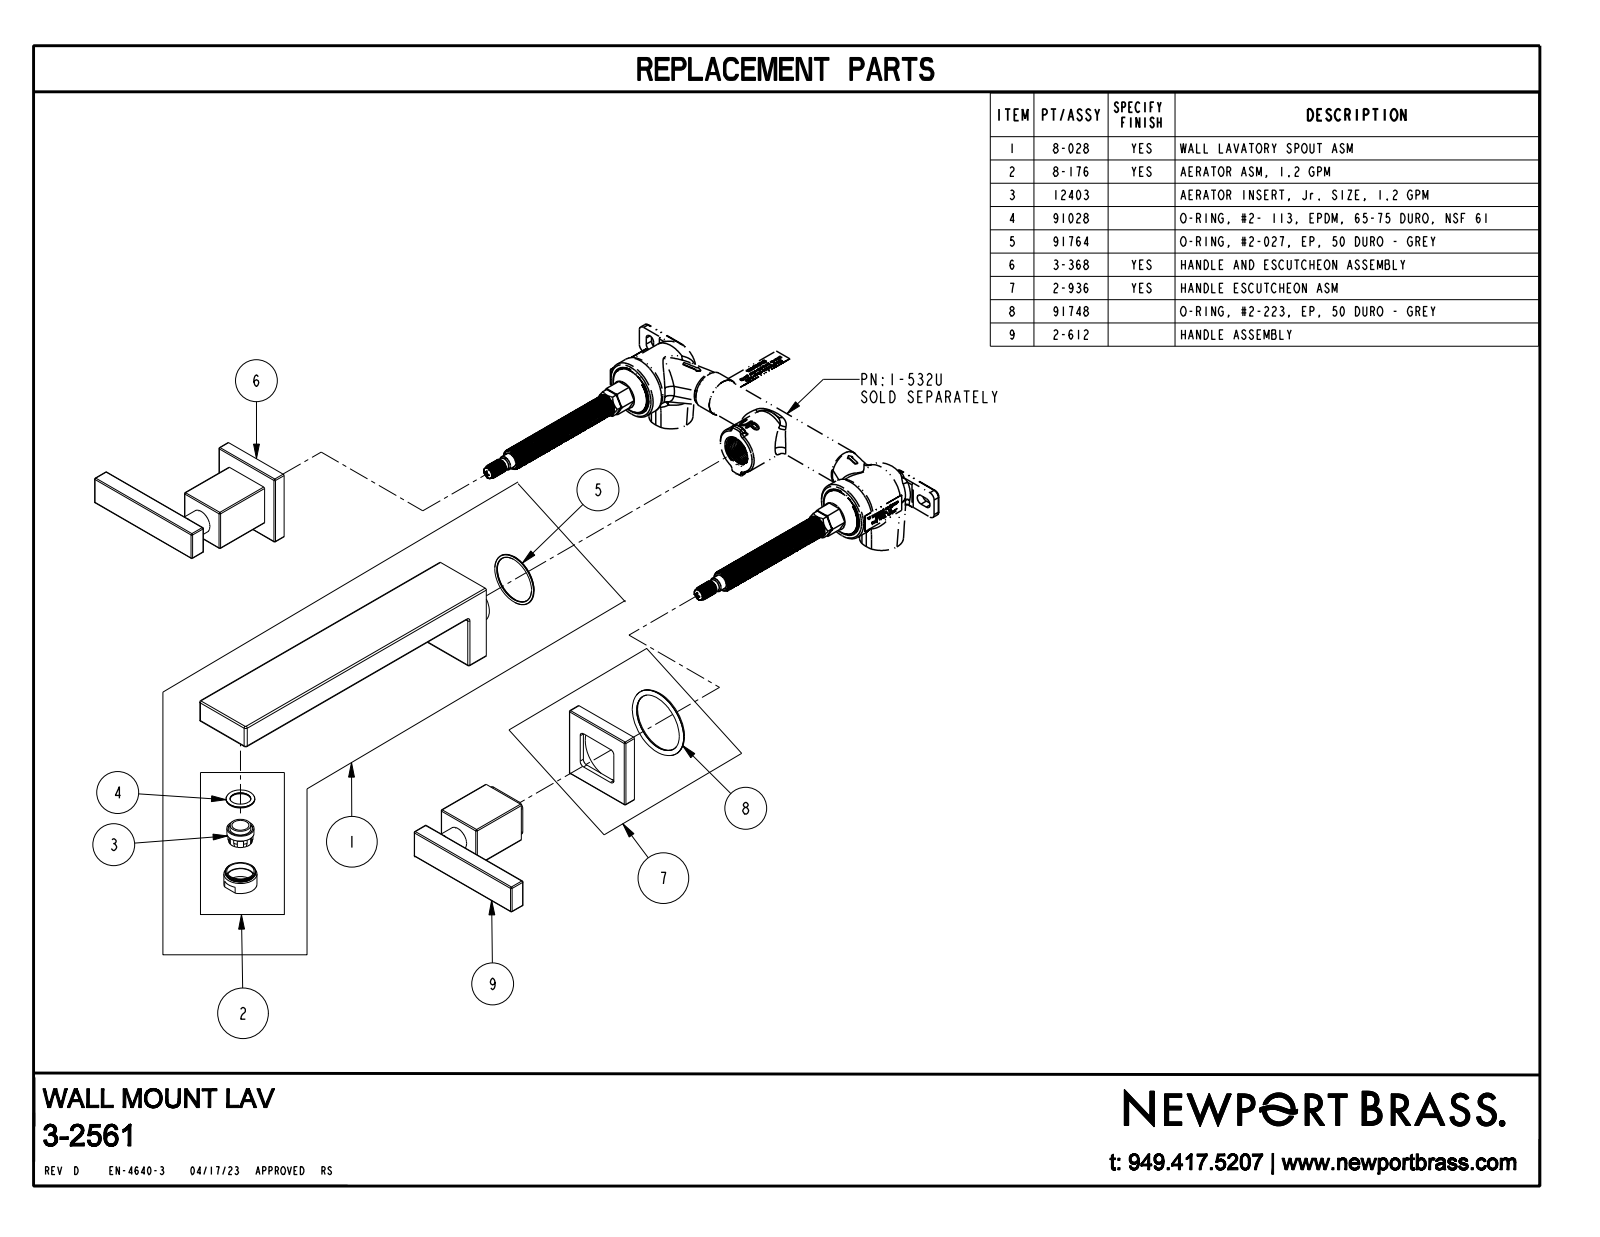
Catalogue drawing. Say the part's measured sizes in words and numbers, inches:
The part is named "3-2561_SW0001". Its 3-D file was written by "CREO PARAMETRIC BY PTC INC, 2018400 (AUTOMOTIVE_DESIGN)". It is 3 solids with 189 faces: 53 planar, 88 cylindrical and 48 other. Overall it measures 13.876 by 9.438 by 2.2 inches. Its volume is 23.84 cubic inches and its surface area 114.1 square inches. Round bosses or shafts: 2 of diameter 0.65, 2 of diameter 0.523, 1 of diameter 1.65, 1 of diameter 1.1, 1 of diameter 0.875. Partial cylindrical surfaces (rounded edges, fillets, slot ends): 48 of radius 0.03, 11 of radius 0.04, 2 of radius 0.06, 1 of radius 0.08. The main face-to-face distances are 0.654, 0.98, 1.75, 0.52, 0.18, 3.05, 1.68, 0.35, 2.7, 0.7.
